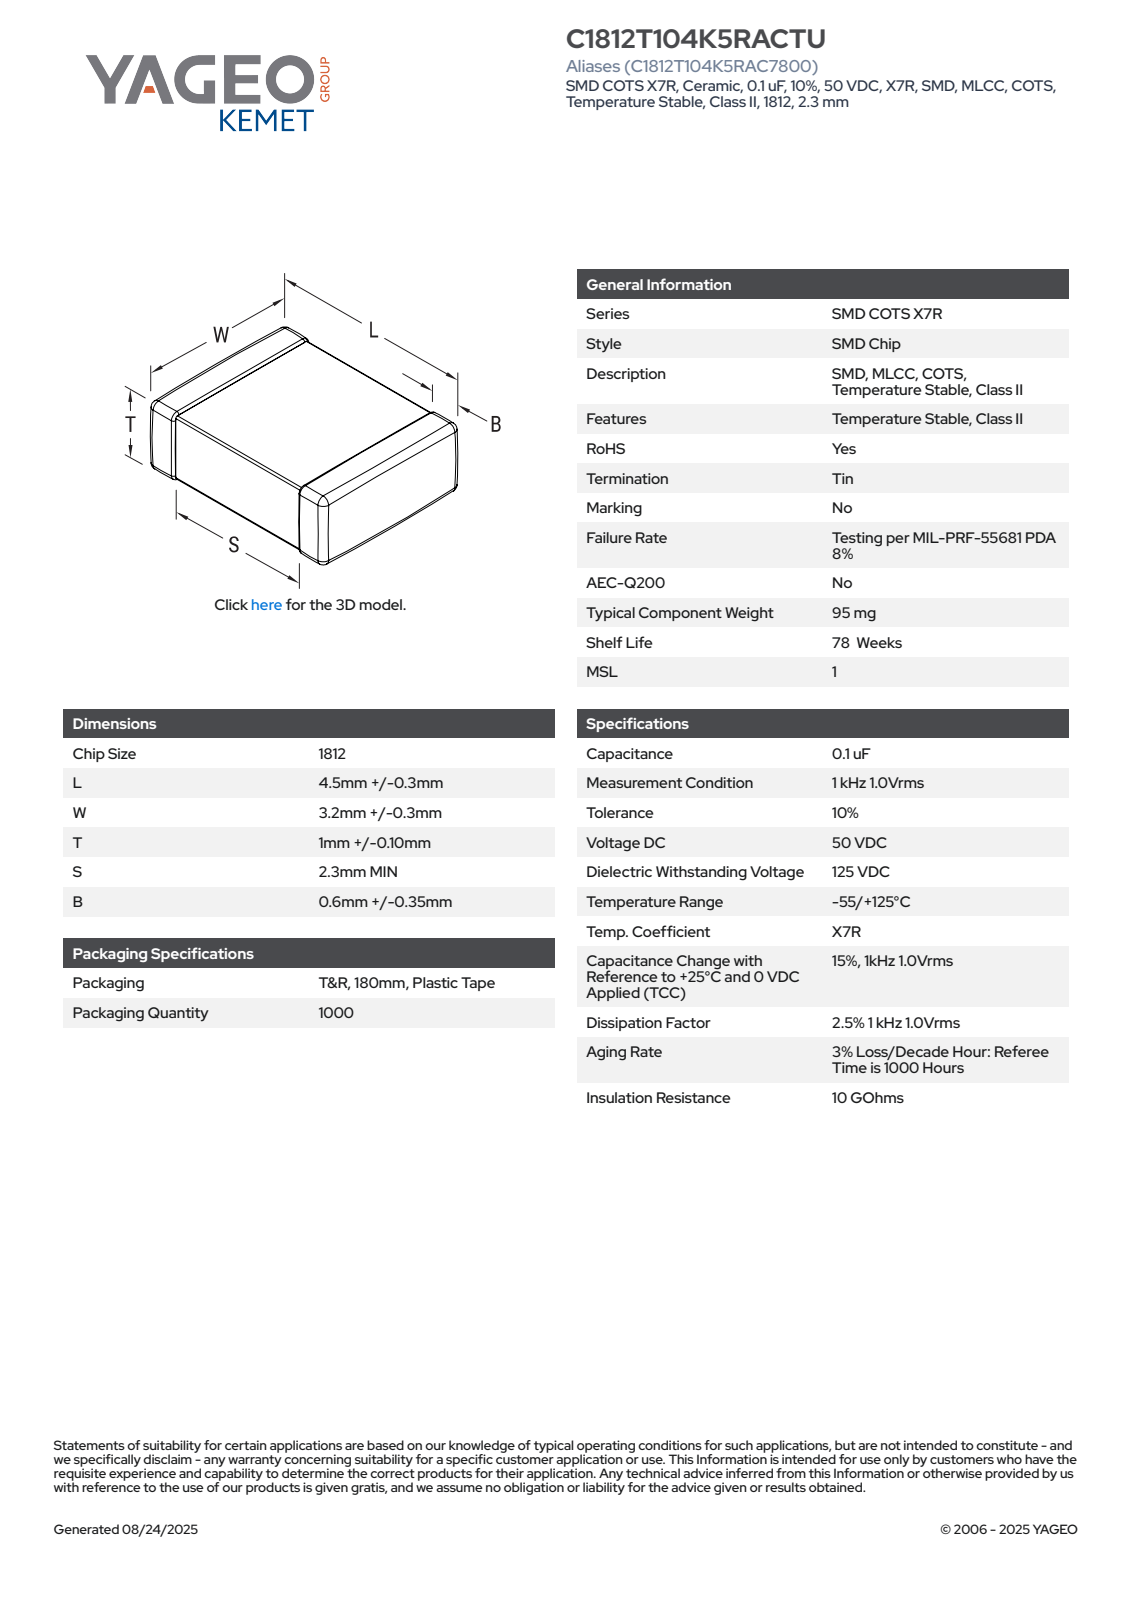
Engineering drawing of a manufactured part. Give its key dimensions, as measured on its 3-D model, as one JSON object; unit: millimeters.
{"part_name": "CCSM_STD_1812_L4.8W3.5T1.1S1B0.95", "step_written_by": "SolidWorks 2021 (AUTOMOTIVE_DESIGN)", "units": "millimeters", "bodies": {"solids": 4, "faces": 121, "planar": 71, "cylindrical": 34, "other": 16}, "overall_size": [4.8, 3.5, 1.1], "volume_mm3": 17, "surface_area_mm2": 51, "face_to_face_distances": [1.03, 0.96, 1.1, 4.8, 3.43, 3.36, 3.5, 2.08, 2.72, 2.59]}
